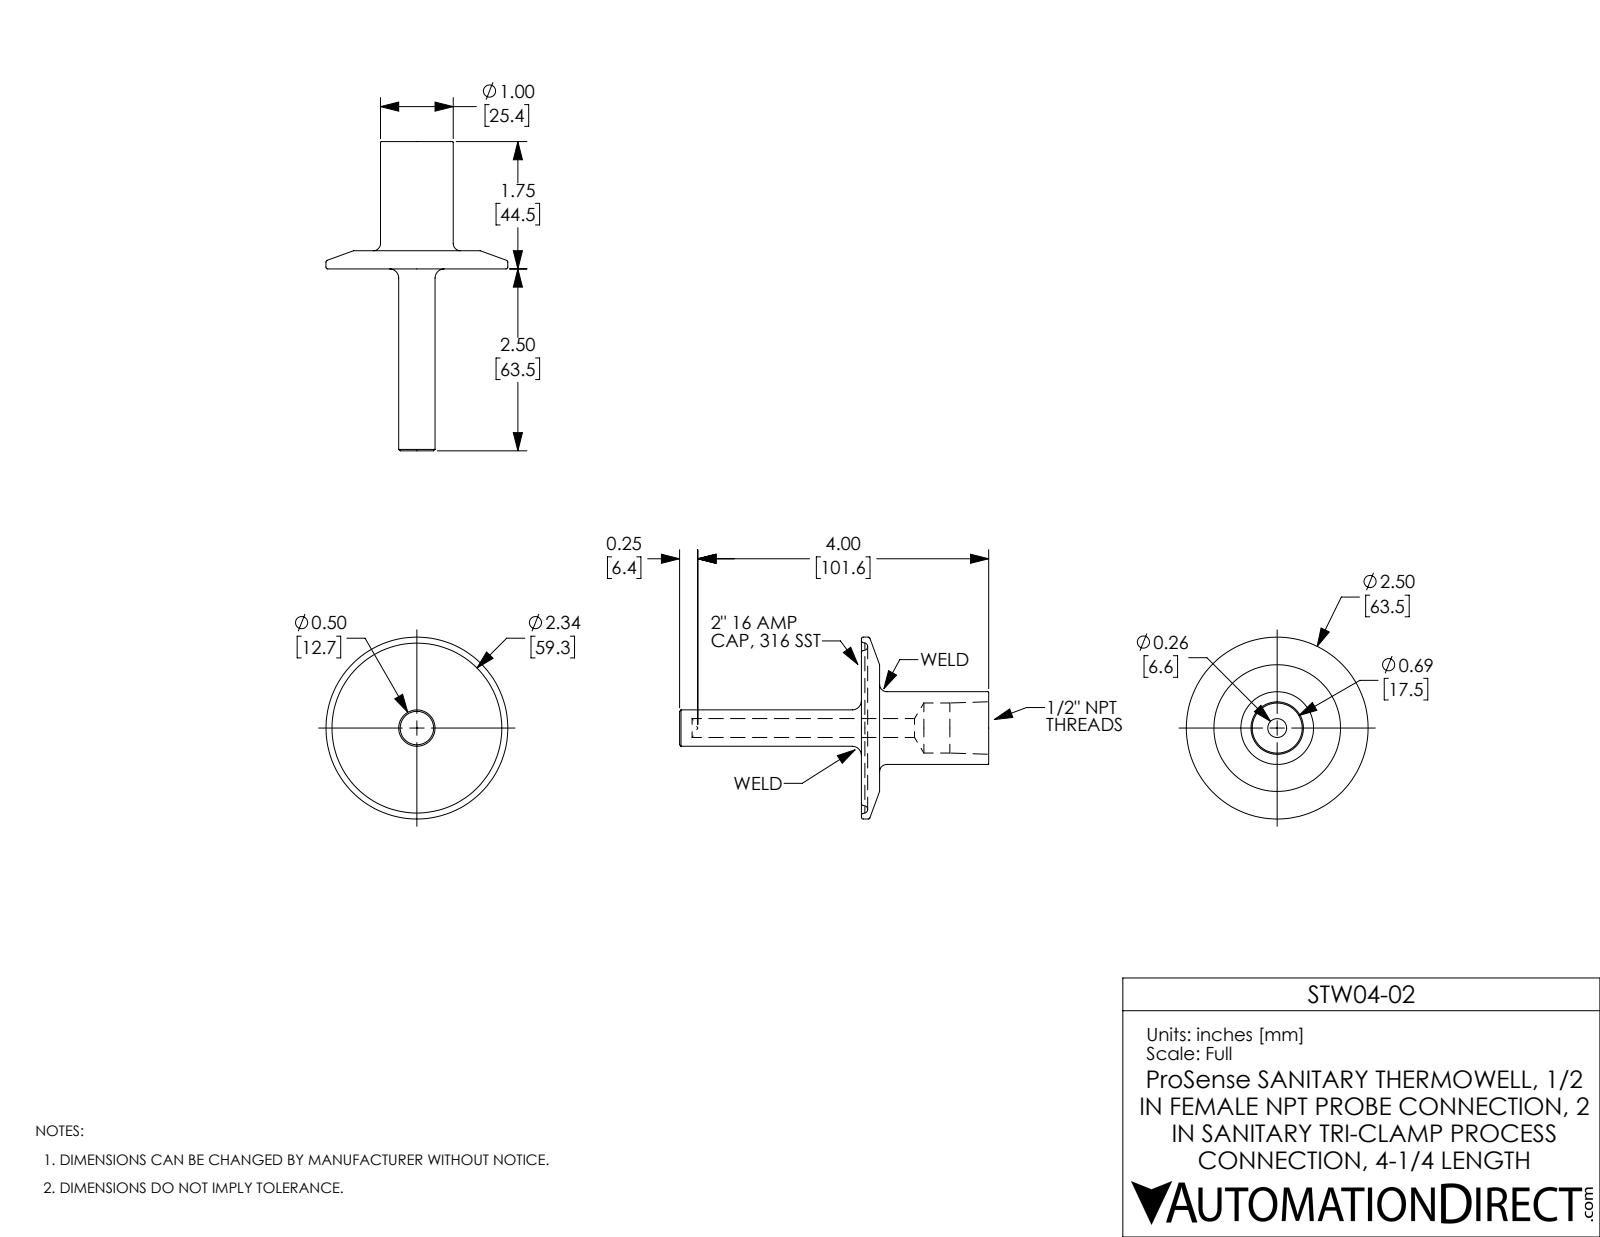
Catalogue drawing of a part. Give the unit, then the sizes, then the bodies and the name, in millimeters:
Units: millimetres
Overall size (bounding box): 108 × 63.5 × 63.5
Round holes (diameter × count): ⌀6.6 ×1, ⌀17.5 ×1
Round bosses / shafts (diameter × count): ⌀63.5 ×1, ⌀25.4 ×1, ⌀12.7 ×1
Main face-to-face distances: 6.4, 38.1, 44.5, 108, 69.9, 63.5
Volume: 35 050 mm³ · Surface area: 15 680 mm²
Bodies: 1 solid, 45 faces (5 planar, 10 cylindrical, 30 other)
Part name (STEP PRODUCT): STW04-02
STEP written by: SolidWorks 2017 (AUTOMOTIVE_DESIGN)
